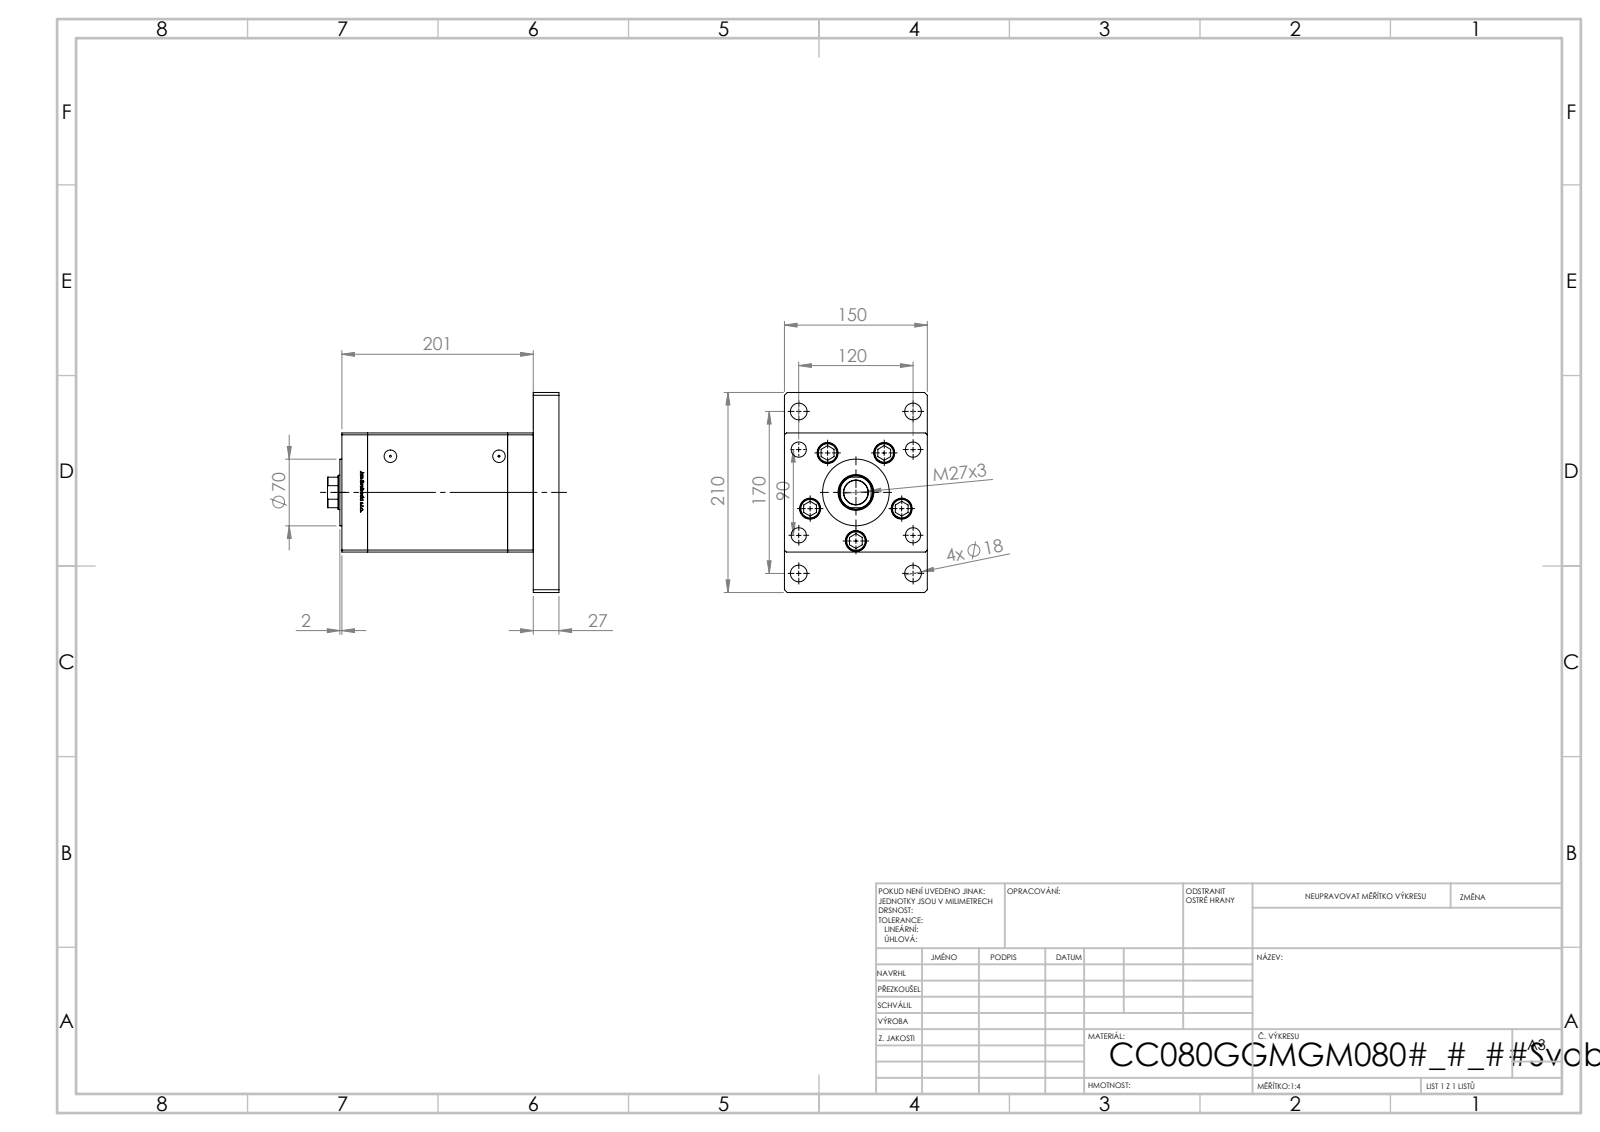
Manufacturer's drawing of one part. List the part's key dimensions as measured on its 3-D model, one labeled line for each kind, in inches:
Part name (STEP PRODUCT): V220C_VC_G; ALLEN BOLT; V220C_FRONT_G; V220C_G_MIDDLE (+2 more)
STEP written by: SolidWorks 2019 (CONFIG_CONTROL_DESIGN)
Units: inches
Bodies: 19 solids, 1313 faces (518 planar, 189 cylindrical, 606 other)
Overall size (bounding box): 9.567 × 8.268 × 5.906
Volume: 246.8 in³ · Surface area: 696.5 in²
Round holes (diameter × count): ⌀0.63 ×9, ⌀0.689 ×9, ⌀0.866 ×5, ⌀0.827 ×4, ⌀0.079 ×2, ⌀0.518 ×2, ⌀1.004 ×1, ⌀1.417 ×1, ⌀1.476 ×1, ⌀4.016 ×1
Round bosses / shafts (diameter × count): ⌀0.315 ×9, ⌀0.827 ×5, ⌀3.15 ×1, ⌀2.756 ×1
Partial cylindrical surfaces — rounded edges, fillets, slot ends (radius × count): R0.037 ×2, R0.689 ×1
Main face-to-face distances: 1.063, 6.85, 7.913, 5.906, 5.787, 4.921, 2.126, 6.594, 0.079, 8.976
Hole centre spacings: 2.008, 1.575, 2.953, 4.096, 4.724, 4.98, 5.118, 6.965
